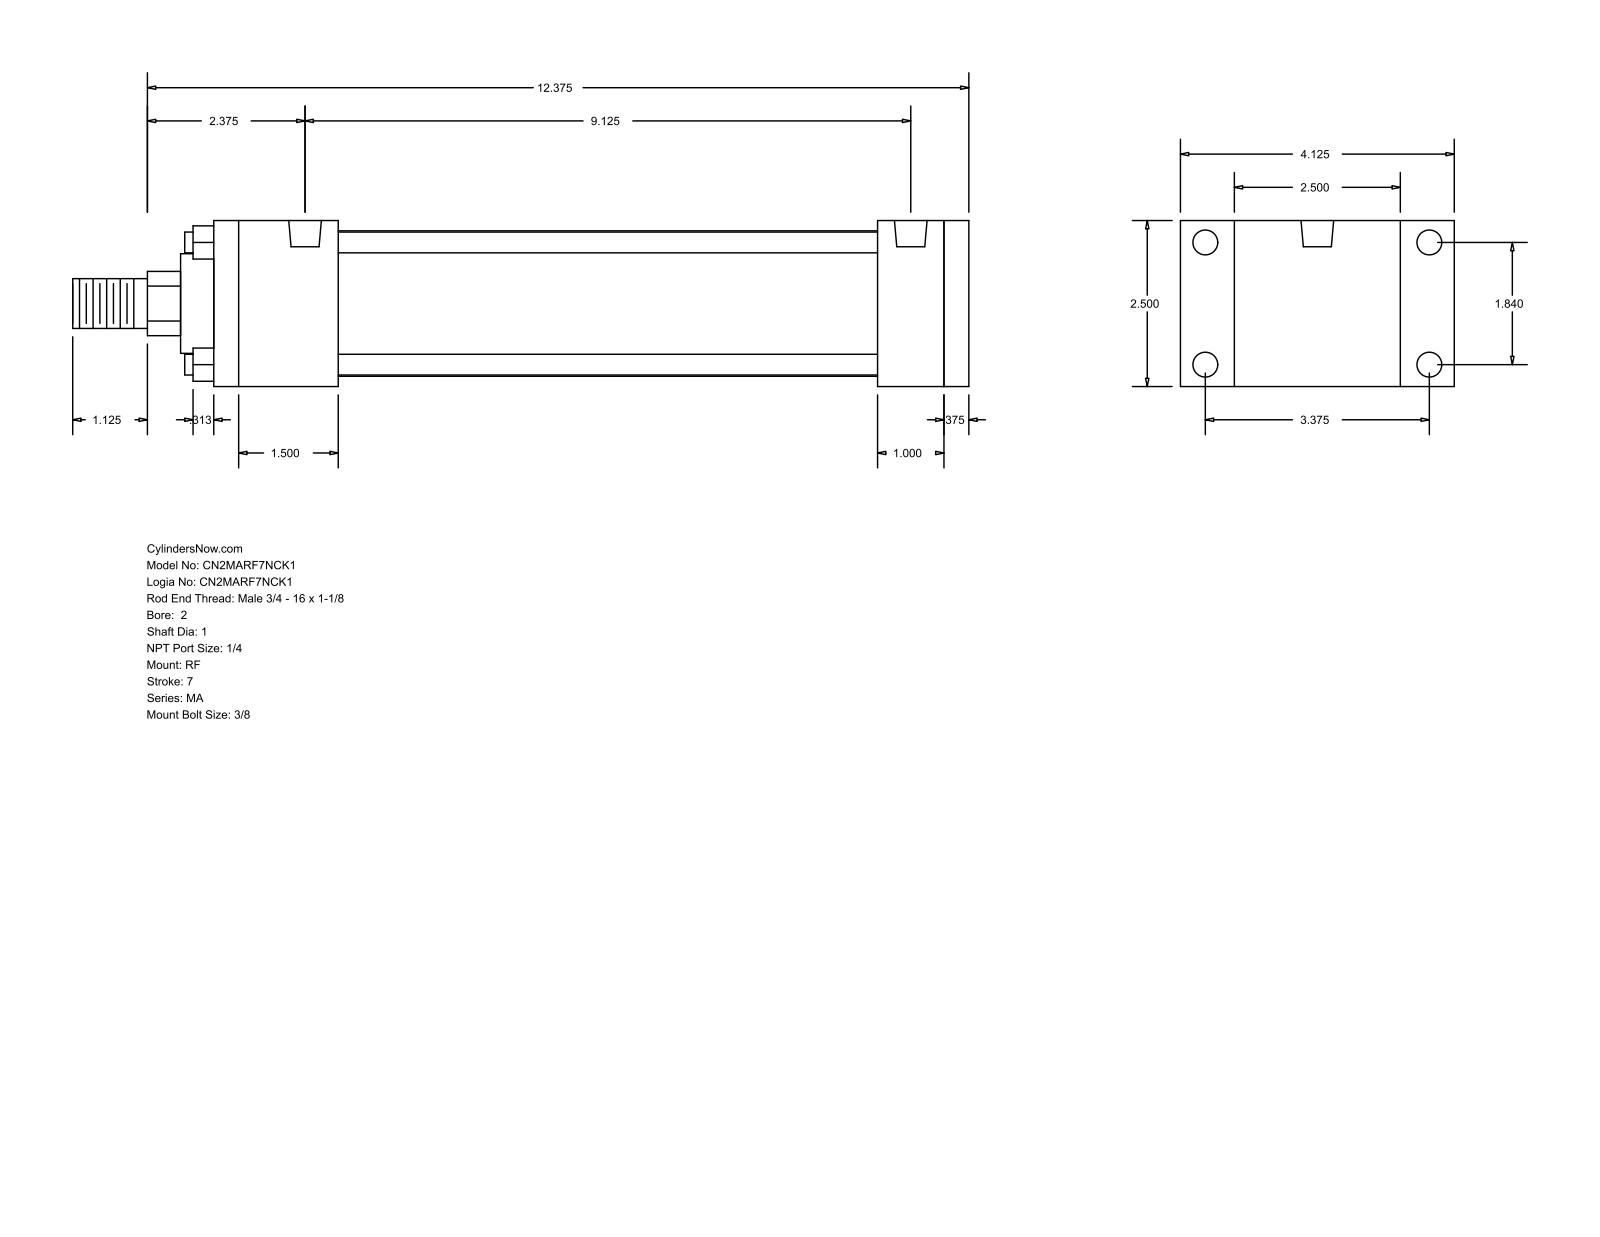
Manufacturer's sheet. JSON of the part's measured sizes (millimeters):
{"part_name": "MA_RF__0200_1", "step_written_by": "GSSL Pune (CONFIG_CONTROL_DESIGN)", "units": "millimeters", "bodies": {"solids": 0, "faces": 92, "planar": 64, "cylindrical": 28, "other": 0}, "overall_size": [342.9, 104.78, 63.5], "round_holes": [[7.94, 4], [9.53, 4], [12.49, 2]], "round_bosses_or_shafts": [[7.94, 4], [55.63, 1], [38.1, 1], [25.4, 1], [19.05, 1]], "partial_cylinders_radius": [[12.29, 1]], "face_to_face_distances": [63.5, 279.4, 9.52, 288.92, 25.4, 20.64, 12.7, 47.63, 231.77, 241.29], "hole_center_spacings": [46.74, 85.72, 97.63, 231.77]}
